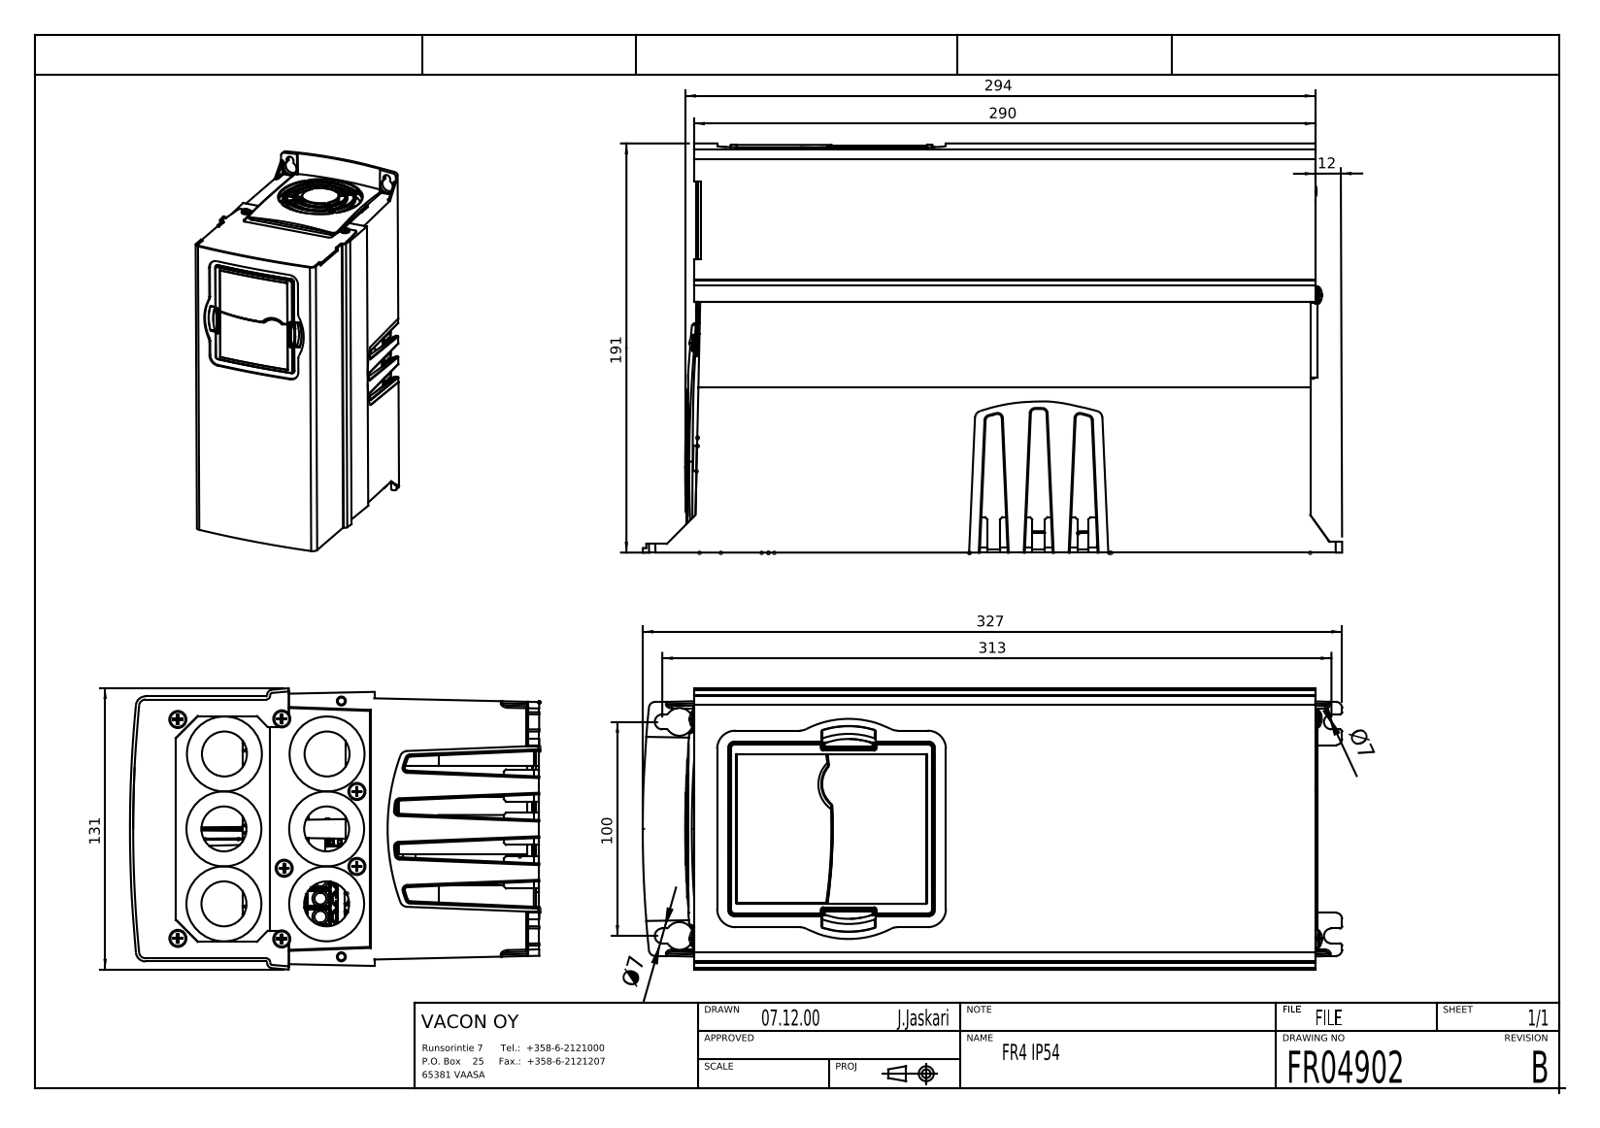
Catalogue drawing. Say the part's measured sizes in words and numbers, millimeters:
The part is named "VACON_FR4_IP54_SB". Its 3-D file was written by "CREO PARAMETRIC BY PTC INC, 2018070 (CONFIG_CONTROL_DESIGN)". It is 1 solid with 3478 faces: 1634 planar, 1036 cylindrical and 808 other. Overall it measures 326.63 by 189.63 by 133.5 millimeters. Its volume is 6 447 000 cubic millimeters and its surface area 900 215 square millimeters. Round holes: 11 of diameter 3.6, 8 of diameter 4.2, 7 of diameter 3, 5 of diameter 4.3, 2 of diameter 0.7, 2 of diameter 1.3, 2 of diameter 3.1, 2 of diameter 5.26, 2 of diameter 9, 2 of diameter 9.3, 2 of diameter 13, 2 of diameter 39. Round bosses or shafts: 4 of diameter 4.2, 3 of diameter 20.3, 3 of diameter 7.6, 3 of diameter 2, 2 of diameter 10, 1 of diameter 66.2, 1 of diameter 50.6, 1 of diameter 35. Partial cylindrical surfaces (rounded edges, fillets, slot ends): 189 of radius 0.5, 83 of radius 1, 76 of radius 1.5, 54 of radius 0.2, 30 of radius 0.3, 24 of radius 2, 22 of radius 4, 19 of radius 3. The main face-to-face distances are 1.5, 9.4, 18.8, 28.2, 37.6, 121, 122.5, 9.39, 47, 18.78. The hole center spacings are 43.22, 56.14, 1.46, 10, 12.07, 15.03, 15.47, 22.28.
